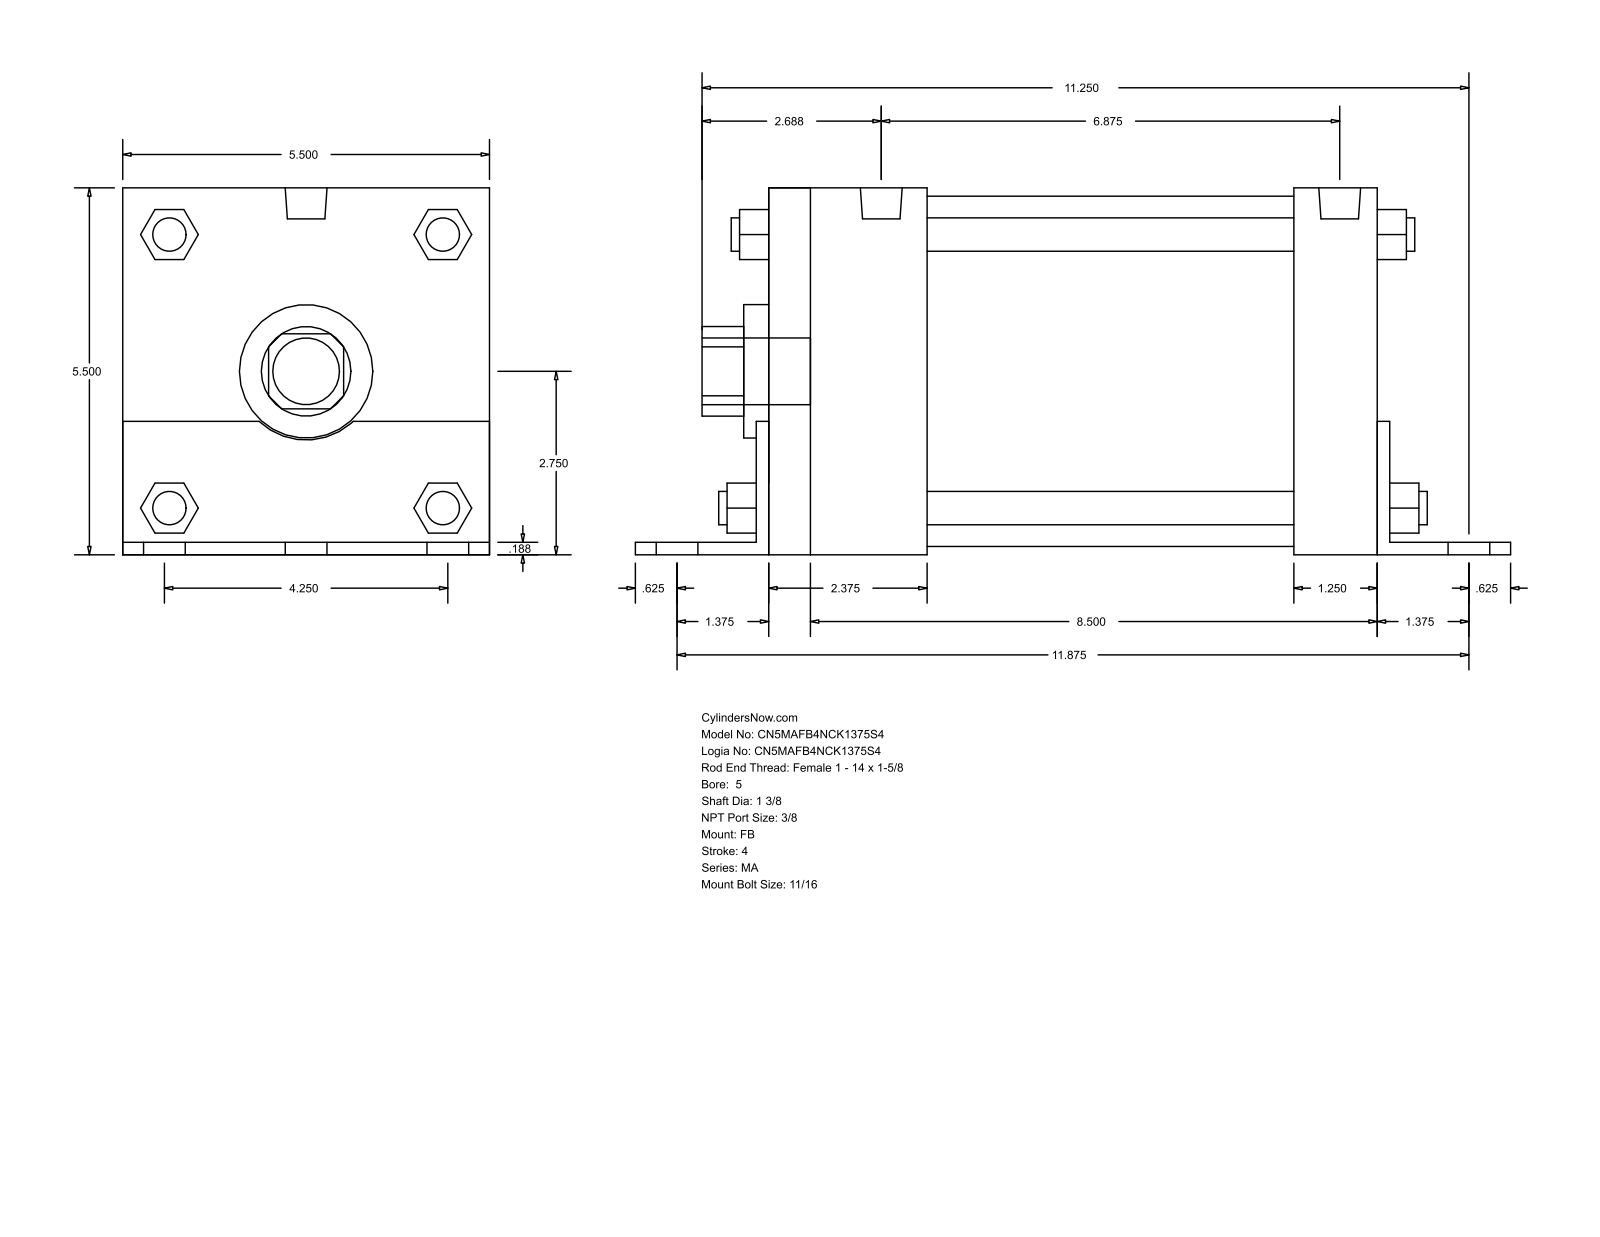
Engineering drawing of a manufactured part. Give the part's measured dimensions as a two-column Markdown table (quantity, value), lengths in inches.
| quantity | value |
| --- | --- |
| part name | MA_FB__0500_1.375 |
| STEP written by | GSSL Pune (CONFIG_CONTROL_DESIGN) |
| units | inches |
| bodies | 0 solids, 140 faces (105 planar, 35 cylindrical, 0 other) |
| overall size | 13.125 × 5.502 × 5.5 |
| round holes (diameter × count) | 1.375 × 1, 2 × 1, 5.25 × 1 |
| round bosses / shafts (diameter × count) | 0.687 × 6, 0.5 × 4, 0.437 × 4, 0.627 × 2, 1 × 1 |
| partial cylindrical surfaces (radius × count) | 0.672 × 1, 1.03 × 1 |
| main face-to-face distances | 5.5, 0.187, 5.502, 9.313, 0.185, 5.315, 9.125, 9.5, 1.25, 1.437 |
